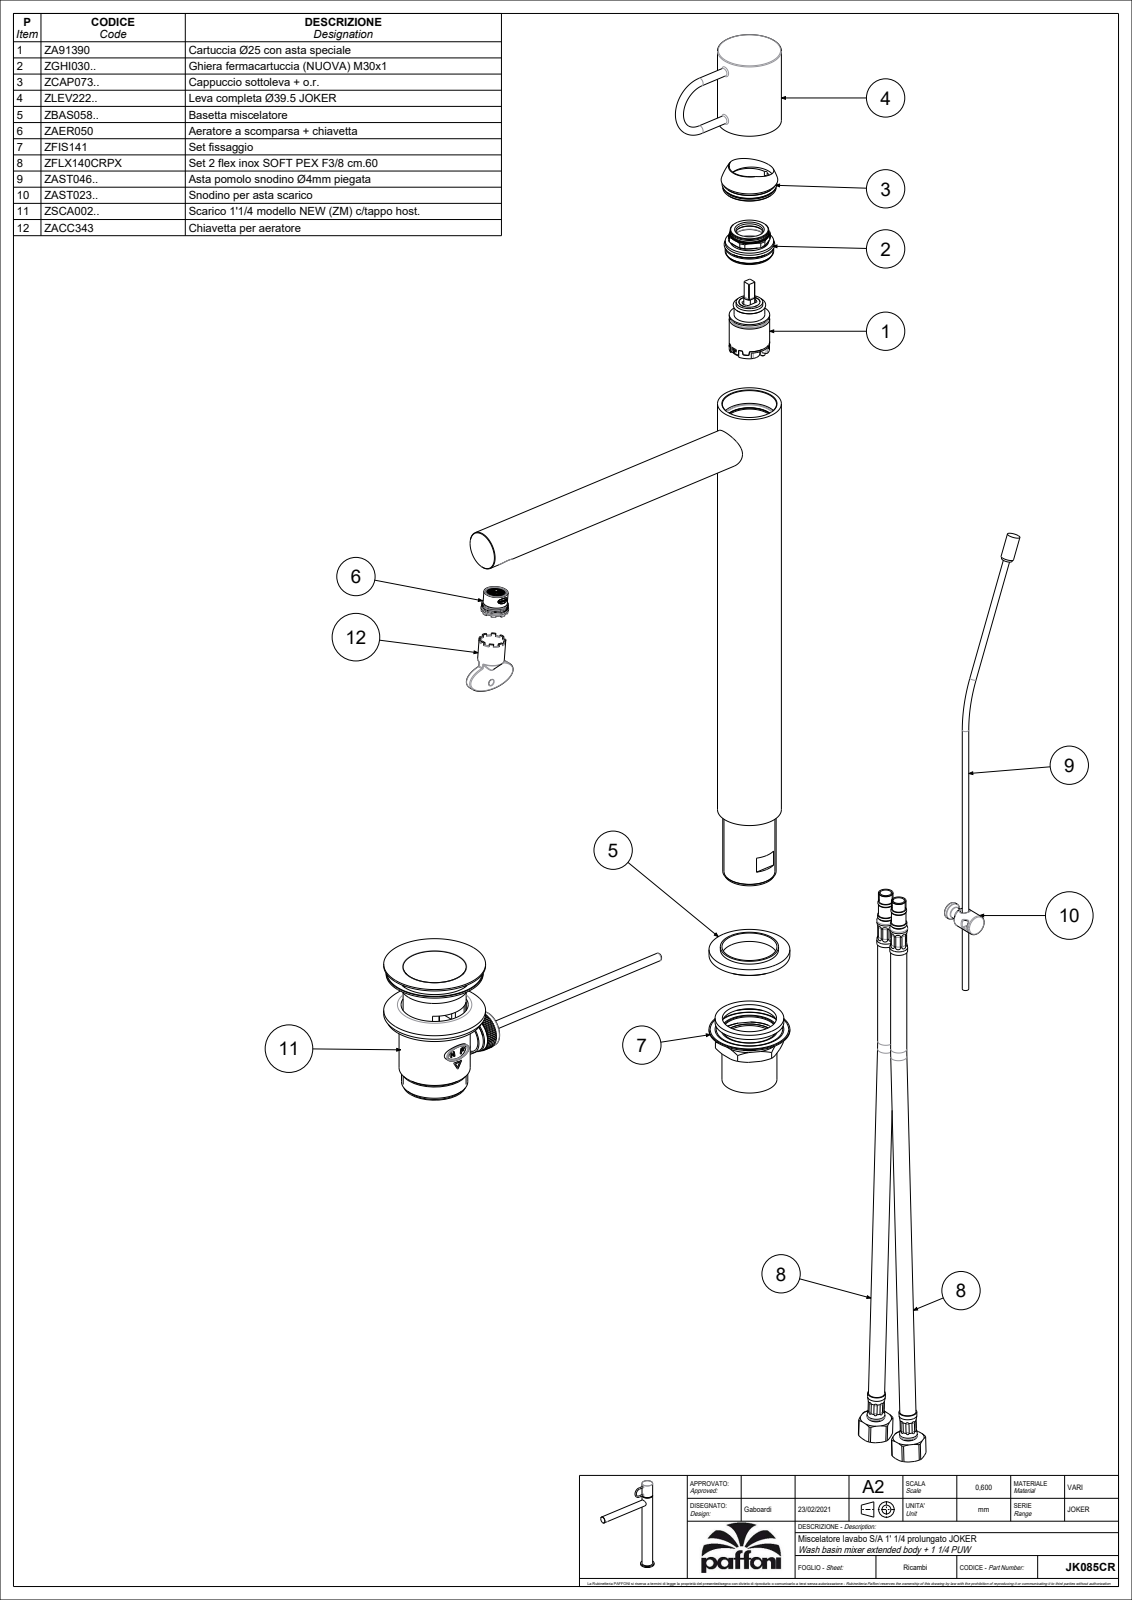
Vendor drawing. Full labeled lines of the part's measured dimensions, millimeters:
Part name (STEP PRODUCT): JK085CR
STEP written by: CREO PARAMETRIC BY PTC INC, 2020044 (CONFIG_CONTROL_DESIGN)
Units: millimetres
Bodies: 2 solids, 2936 faces (1937 planar, 631 cylindrical, 368 other)
Overall size (bounding box): 346.85 × 251.38 × 50
Volume: 224 492 mm³ · Surface area: 153 899 mm²
Round holes (diameter × count): ⌀6.5 ×4, ⌀5 ×3, ⌀7 ×3, ⌀3.2 ×2, ⌀9.4 ×2, ⌀11 ×2, ⌀3 ×1, ⌀4.2 ×1, ⌀5.5 ×1, ⌀8 ×1, ⌀12.15 ×1, ⌀12.45 ×1
Round bosses / shafts (diameter × count): ⌀10 ×4, ⌀4 ×3, ⌀0.9 ×3, ⌀11 ×2, ⌀9 ×2, ⌀8 ×2, ⌀5 ×2, ⌀50 ×1
Partial cylindrical surfaces — rounded edges, fillets, slot ends (radius × count): R0.12 ×51, R3 ×28, R0.5 ×18, R0.2 ×8, R0.6 ×5, R1 ×5, R2 ×4, R3.5 ×3
Main face-to-face distances: 2, 4, 344.5, 340.5, 50.5, 6.5, 243.5, 239.5, 101, 14.8
Hole centre spacings: 1.5, 6.72, 7.85, 8.92, 8.94, 9.33, 11, 15.46
